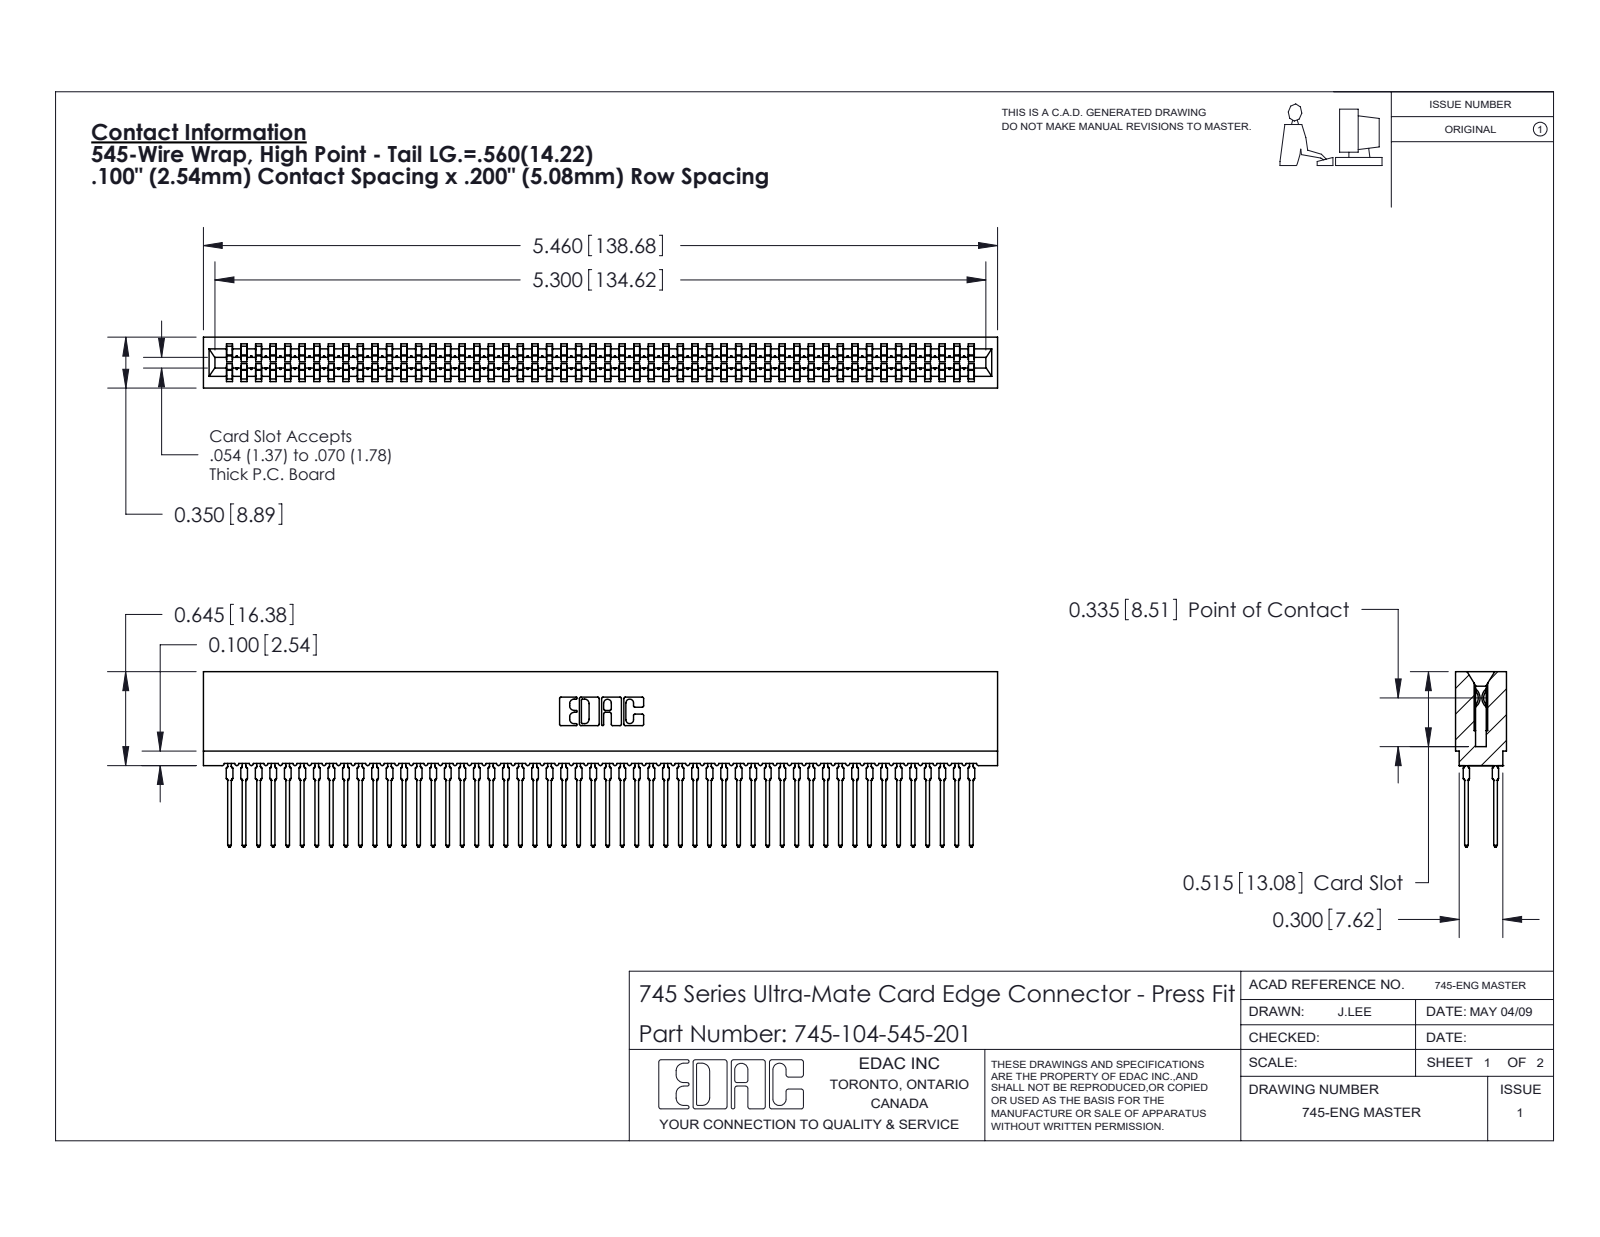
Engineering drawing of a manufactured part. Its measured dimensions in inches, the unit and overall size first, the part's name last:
Units: inches
Overall size (bounding box): 5.46 × 1.206 × 0.35
Partial cylindrical surfaces — rounded edges, fillets, slot ends (radius × count): R0.021 ×208, R0.015 ×104, R0.01 ×22, R0.005 ×8, R0.011 ×8, R0.007 ×6, R0.031 ×6, R0.026 ×3
Main face-to-face distances: 0.063, 0.287, 0.35, 0.2, 0.045, 0.305, 0.018, 0.243, 0.138, 0.212
Volume: 0.781 in³ · Surface area: 43.13 in²
Bodies: 105 solids, 9403 faces (4839 planar, 1860 cylindrical, 2704 other)
Part name (STEP PRODUCT): 745-292-001_545; 745 Part_Insulator Option - 01; 745-104-545-201
STEP written by: SolidWorks 2020 (CONFIG_CONTROL_DESIGN)
